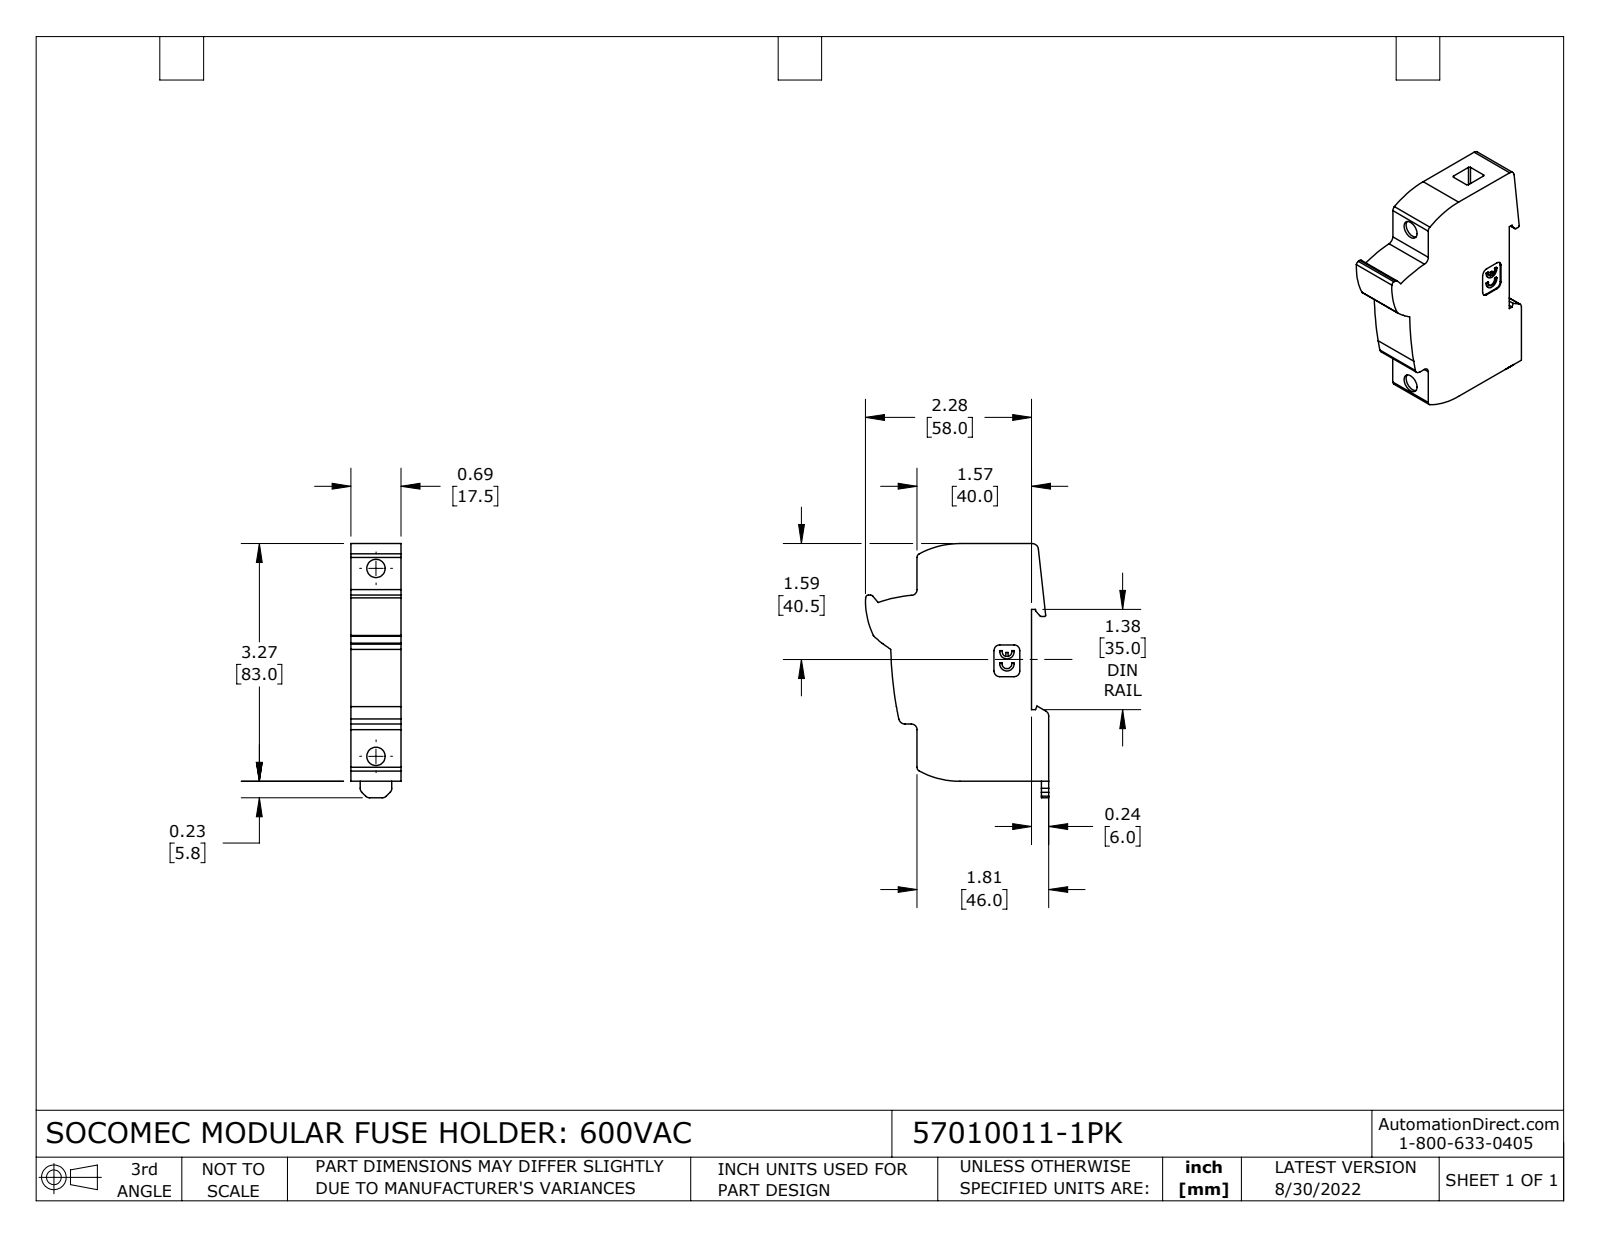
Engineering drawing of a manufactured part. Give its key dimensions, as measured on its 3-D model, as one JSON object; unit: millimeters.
{"part_name": "57010011-1PK", "step_written_by": "SolidWorks 2021 (CONFIG_CONTROL_DESIGN)", "units": "millimeters", "bodies": {"solids": 1, "faces": 105, "planar": 52, "cylindrical": 53, "other": 0}, "overall_size": [88.8, 64, 17.5], "volume_mm3": 69300, "surface_area_mm2": 13760, "round_holes": [[6.4, 2]], "partial_cylinders_radius": [[2, 11], [0.5, 5], [1, 4], [1.5, 2], [1.7, 2], [2.2, 2], [2.5, 2], [30.1, 2]], "face_to_face_distances": [17.5, 6, 40, 83, 46, 5.1, 12.4, 7.4, 13.2, 7.1], "hole_center_spacings": [65.6]}
